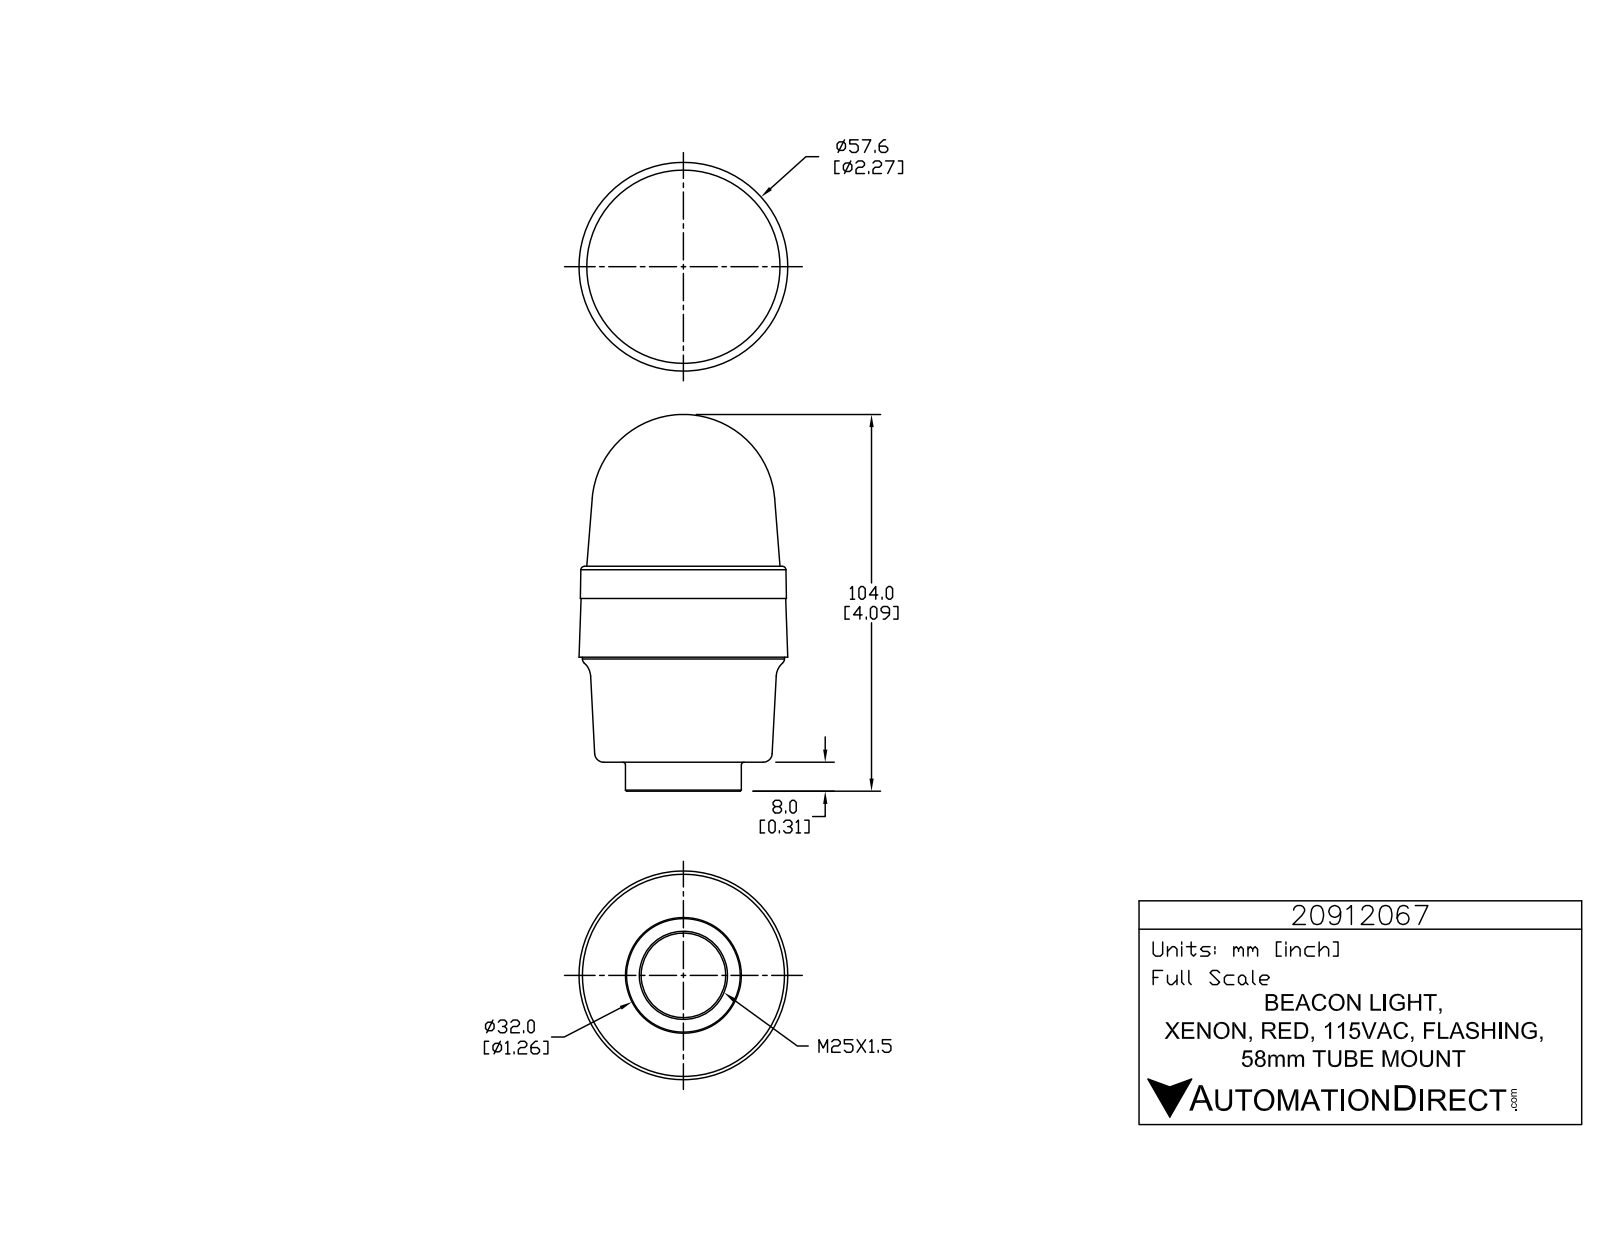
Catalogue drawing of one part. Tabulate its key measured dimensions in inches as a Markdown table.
| quantity | value |
| --- | --- |
| part name | 20912067 |
| STEP written by | SolidWorks 2015 (AUTOMOTIVE_DESIGN) |
| units | inches |
| bodies | 1 solid, 791 faces (525 planar, 168 cylindrical, 98 other) |
| overall size | 4.051 × 2.269 × 2.269 |
| volume | 11.72 in³ |
| surface area | 29.93 in² |
| round holes (diameter × count) | 0.039 × 3, 0.92 × 1 |
| round bosses / shafts (diameter × count) | 0.226 × 3, 0.056 × 3, 2.197 × 1, 1.26 × 1 |
| partial cylindrical surfaces (radius × count) | 0.008 × 6, 0.008 × 6, 0.008 × 6, 0.131 × 6, 0.004 × 3, 0.005 × 3, 0.008 × 3, 0.008 × 3 |
| main face-to-face distances | 0.315, 1.142, 1.457, 0.988, 2.13, 2.445, 0.35, 0.638, 1.78, 2.094 |
